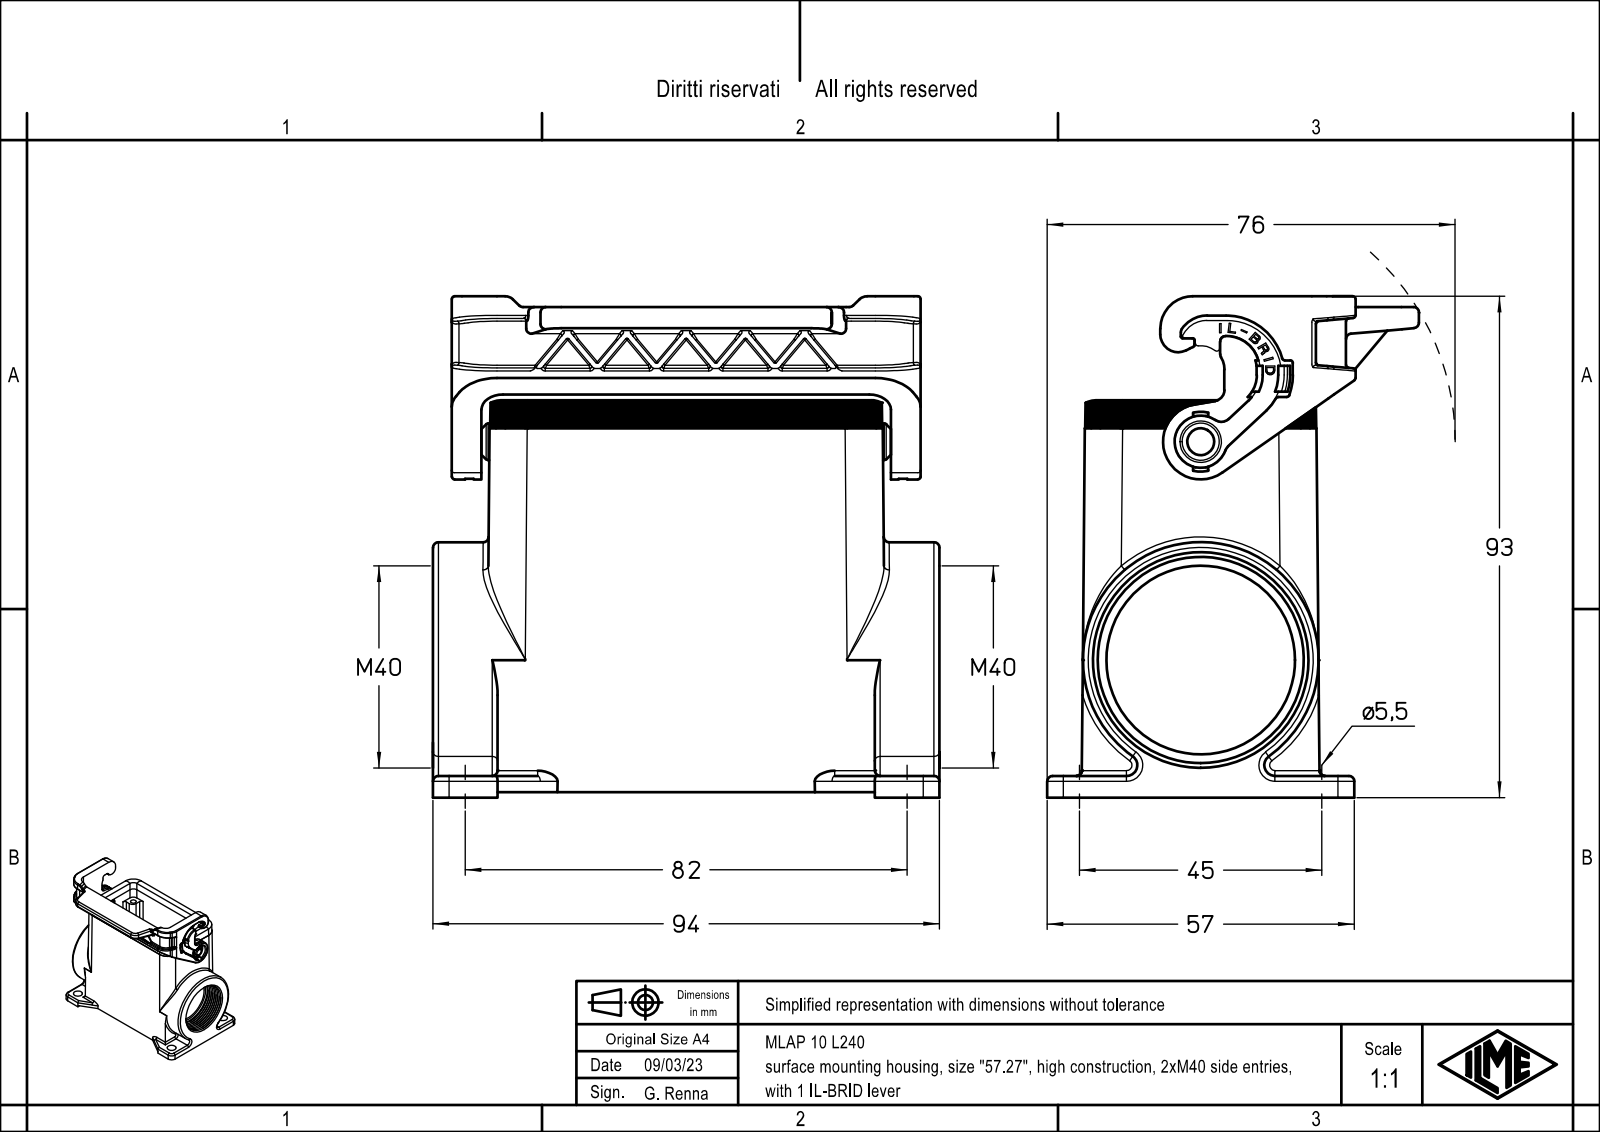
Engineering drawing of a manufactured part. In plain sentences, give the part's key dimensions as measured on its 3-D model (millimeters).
The part is named "MLAP 10 L232; MLAP 10 L240". Its 3-D file was written by "Creo Elements/Direct Modeling 20.1B 02-Apr-2019 (C) Parametric Technology GmbH (AUTOMOTIVE_DESIGN)". It is 1 solid with 1009 faces: 623 planar, 290 cylindrical and 96 other. Overall it measures 94 by 93 by 69 millimeters. Its volume is 101 181 cubic millimeters and its surface area 54 906 square millimeters. Round holes: 4 of diameter 3, 4 of diameter 3.5, 4 of diameter 5.5, 1 of diameter 3.25, 1 of diameter 5.4, 1 of diameter 7.7, 1 of diameter 28, 1 of diameter 32, 1 of diameter 38.5. Round bosses or shafts: 1 of diameter 43.75, 1 of diameter 6.9, 1 of diameter 6.8, 1 of diameter 5.2, 1 of diameter 3.2. Partial cylindrical surfaces (rounded edges, fillets, slot ends): 27 of radius 0.1, 16 of radius 3, 15 of radius 0.2, 14 of radius 1, 11 of radius 0.5, 11 of radius 2, 10 of radius 7, 9 of radius 1.5. The main face-to-face distances are 3, 87, 1, 4, 91, 5.5, 81.5, 7, 90, 14. The hole center spacings are 15.4, 38.11, 70.08, 78.27, 27, 45, 57, 63.07.
